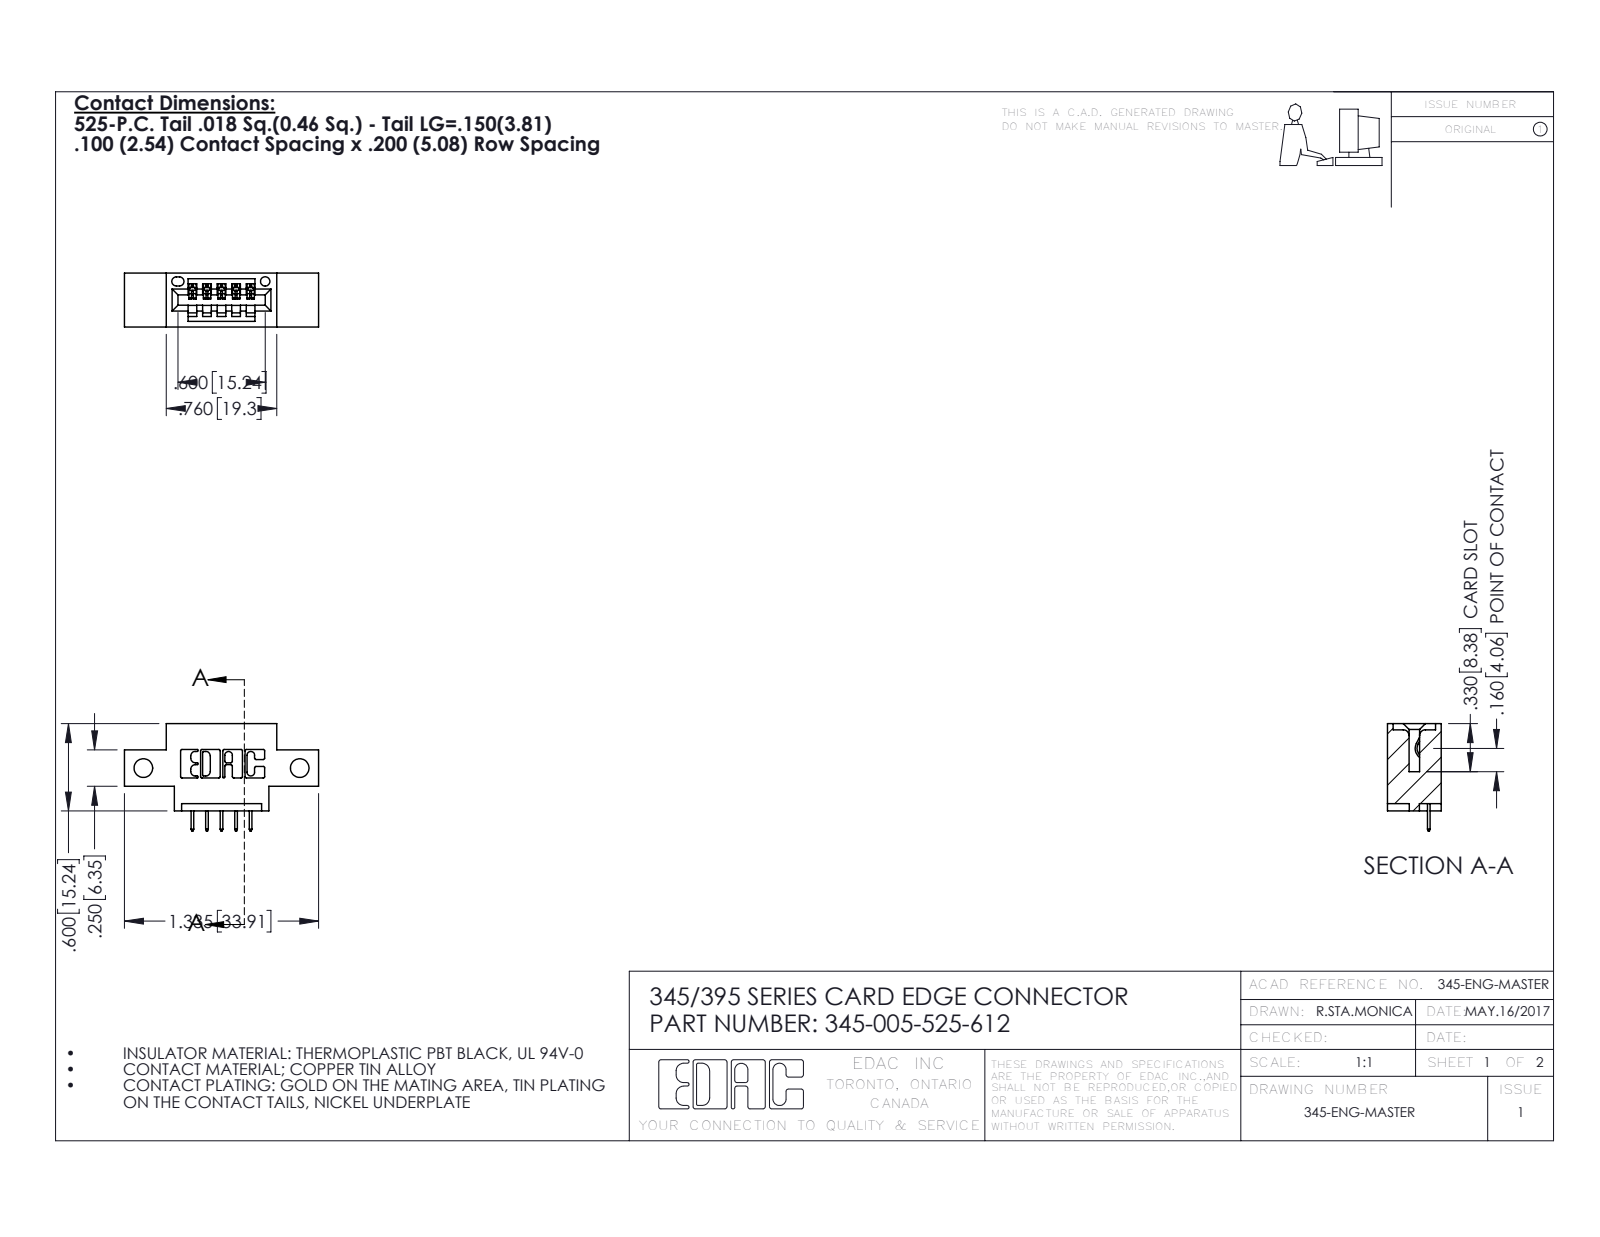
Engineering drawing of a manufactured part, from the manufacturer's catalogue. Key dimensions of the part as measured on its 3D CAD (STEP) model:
Part name (STEP PRODUCT): 345-292-001_345-293-125; 345-005-525-612; 345 Part_0.170 Offset - Side Mount
STEP written by: SolidWorks 2020 (CONFIG_CONTROL_DESIGN)
Units: inches
Bodies: 6 solids, 440 faces (314 planar, 126 cylindrical, 0 other)
Overall size (bounding box): 1.335 × 0.737 × 0.37
Volume: 0.165 in³ · Surface area: 4.645 in²
Round holes (diameter × count): ⌀0.128 ×2, ⌀0.064 ×1
Partial cylindrical surfaces — rounded edges, fillets, slot ends (radius × count): R0.01 ×22, R0.006 ×10, R0.007 ×6, R0.031 ×6, R0.026 ×3, R0.031 ×2, R0.04 ×2, R0.014 ×1
Main face-to-face distances: 0.37, 0.2, 0.1, 0.072, 0.298, 0.25, 0.025, 0.06, 0.55, 0.15
Hole centre spacings: 1.075
